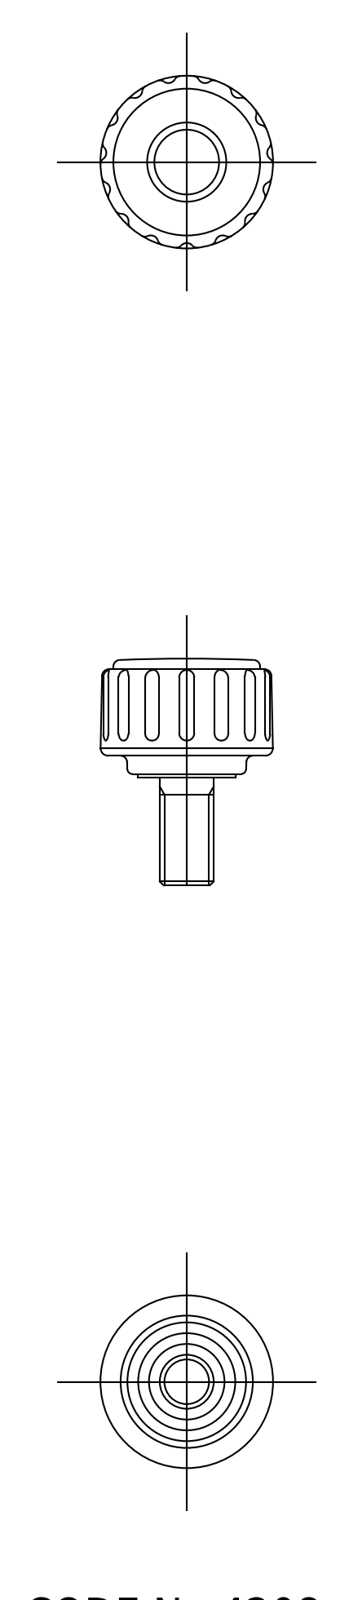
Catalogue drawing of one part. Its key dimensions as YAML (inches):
part_name: "67115029; 67115042"
step_written_by: "CADfix (AUTOMOTIVE_DESIGN)"
units: inches
bodies: {solids: 2, faces: 70, planar: 0, cylindrical: 0, other: 70}
overall_size: [0.825, 0.629, 0.629]
volume: 0.123
surface_area: 2.062
